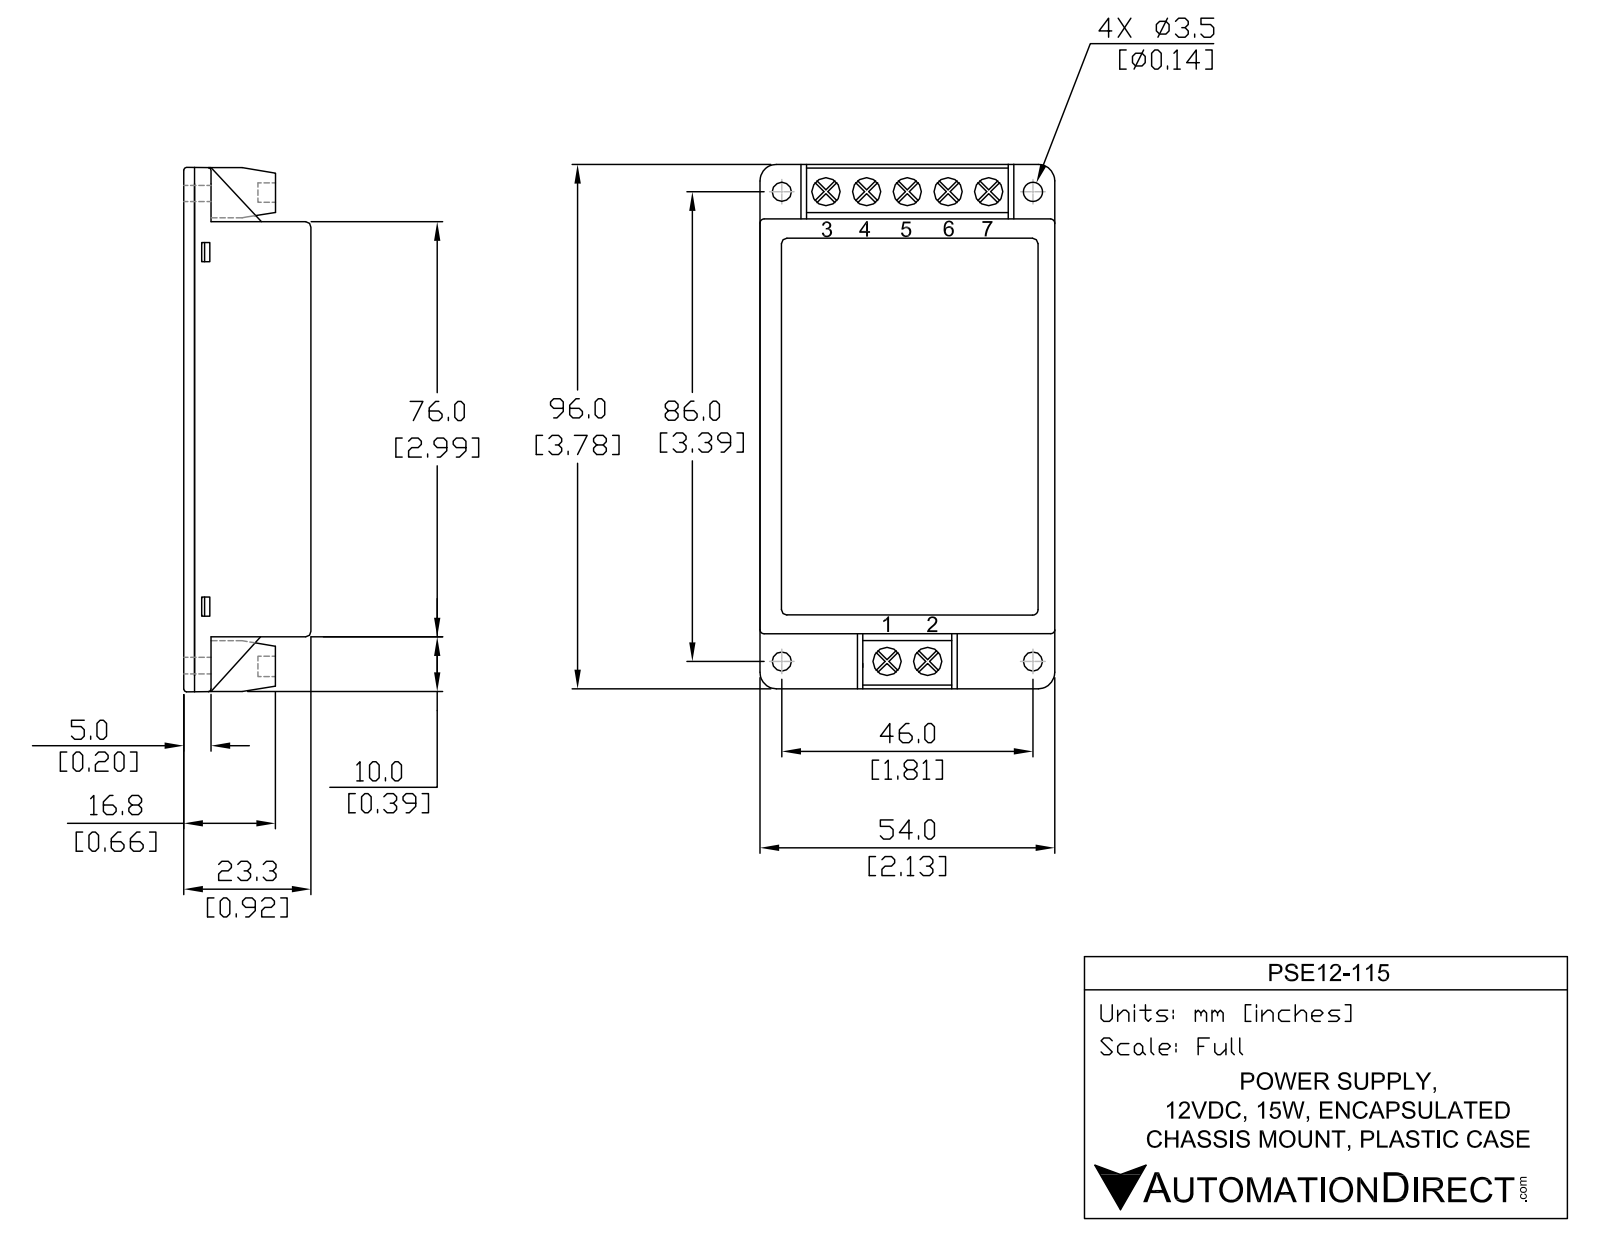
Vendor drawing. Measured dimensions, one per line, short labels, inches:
name: PSE12-115
written by: SolidWorks 2011 (CONFIG_CONTROL_DESIGN)
unit: in
bodies: 2 solids, 369 faces (246 planar, 62 cylindrical, 61 other)
size: 3.78 × 2.13 × 0.92
volume: 6.464 in³; area: 45.54 in²
holes: 7× ⌀0.2, 4× ⌀0.14
rounds: 20× R0.03, 4× R0.125
face distances: 0.078, 0.08, 0.84, 0.918, 0.838, 2.13, 2.99, 0.92, 0.842, 0.015
hole spacings: 0.26, 0.52, 0.26, 0.775, 1.035, 1.81, 3.362, 3.363
